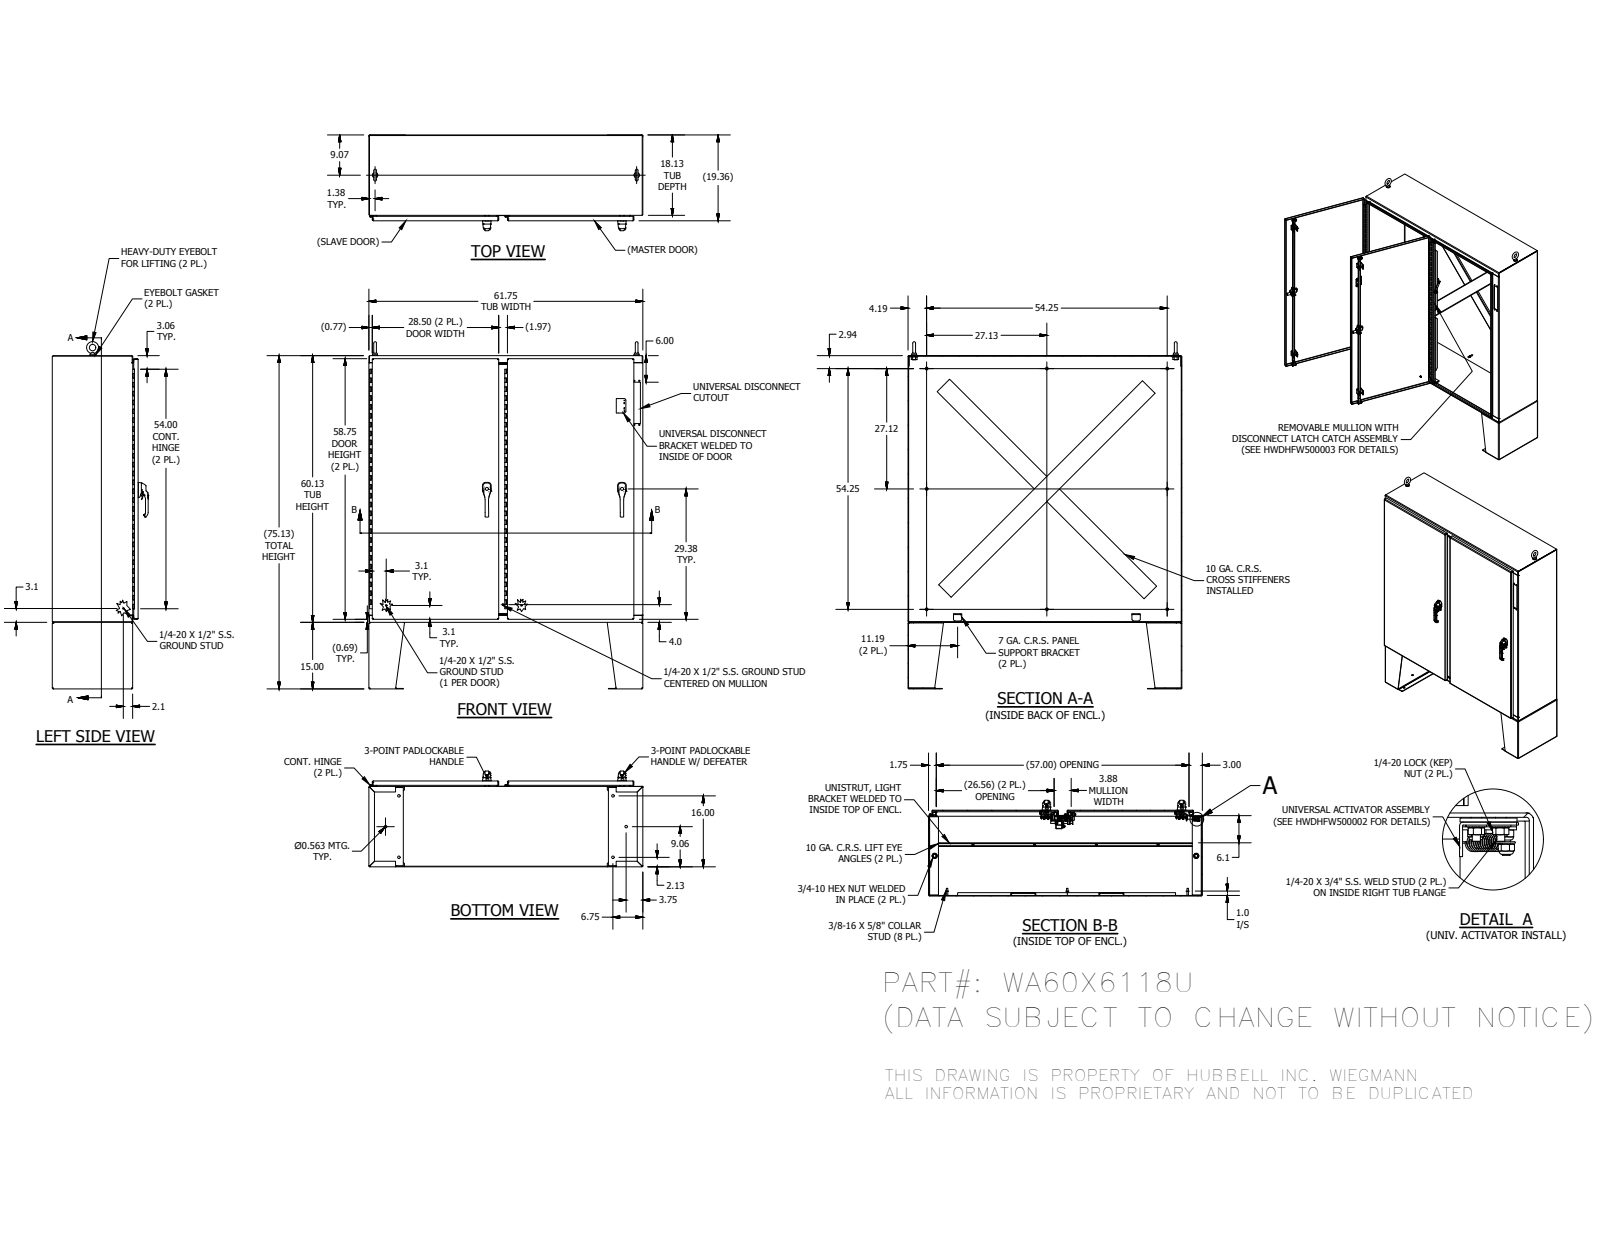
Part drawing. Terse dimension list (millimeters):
name: WA60X6118UBLR; WAX6118UTOP; WAX6118UBTM; HFW332010S (+8 more)
written by: Autodesk Inventor 2016 (AUTOMOTIVE_DESIGN)
unit: mm
bodies: 215 solids, 8753 faces (4044 planar, 2948 cylindrical, 1761 other)
size: 1987.49 × 1568.45 × 548.85
volume: 34 230 000 mm³; area: 20 960 000 mm²
holes: 19× ⌀6.35, 18× ⌀9.52, 18× ⌀14.29, 8× ⌀4.83, 8× ⌀5.08, 8× ⌀5.16, 8× ⌀7.02, 8× ⌀7.33, 8× ⌀7.94, 8× ⌀8.51, 8× ⌀9.65, 7× ⌀5.11
bosses: 23× ⌀6.35, 18× ⌀8.38, 13× ⌀15.88, 12× ⌀8.56, 11× ⌀9.52, 9× ⌀25.4, 9× ⌀14.29, 8× ⌀11.13
rounds: 341× R0.5, 203× R0.3, 192× R0.51, 44× R0.47, 40× R1.27, 37× R3.17, 35× R2.38, 27× R1.59
face distances: 3.4, 488.1, 484.7, 491.5, 3.41, 1523.77, 1565.04, 3.18, 1520.36, 1561.64
hole spacings: 0.77, 50.8, 773.9, 0.78, 774.23, 27.99, 28, 40.66
